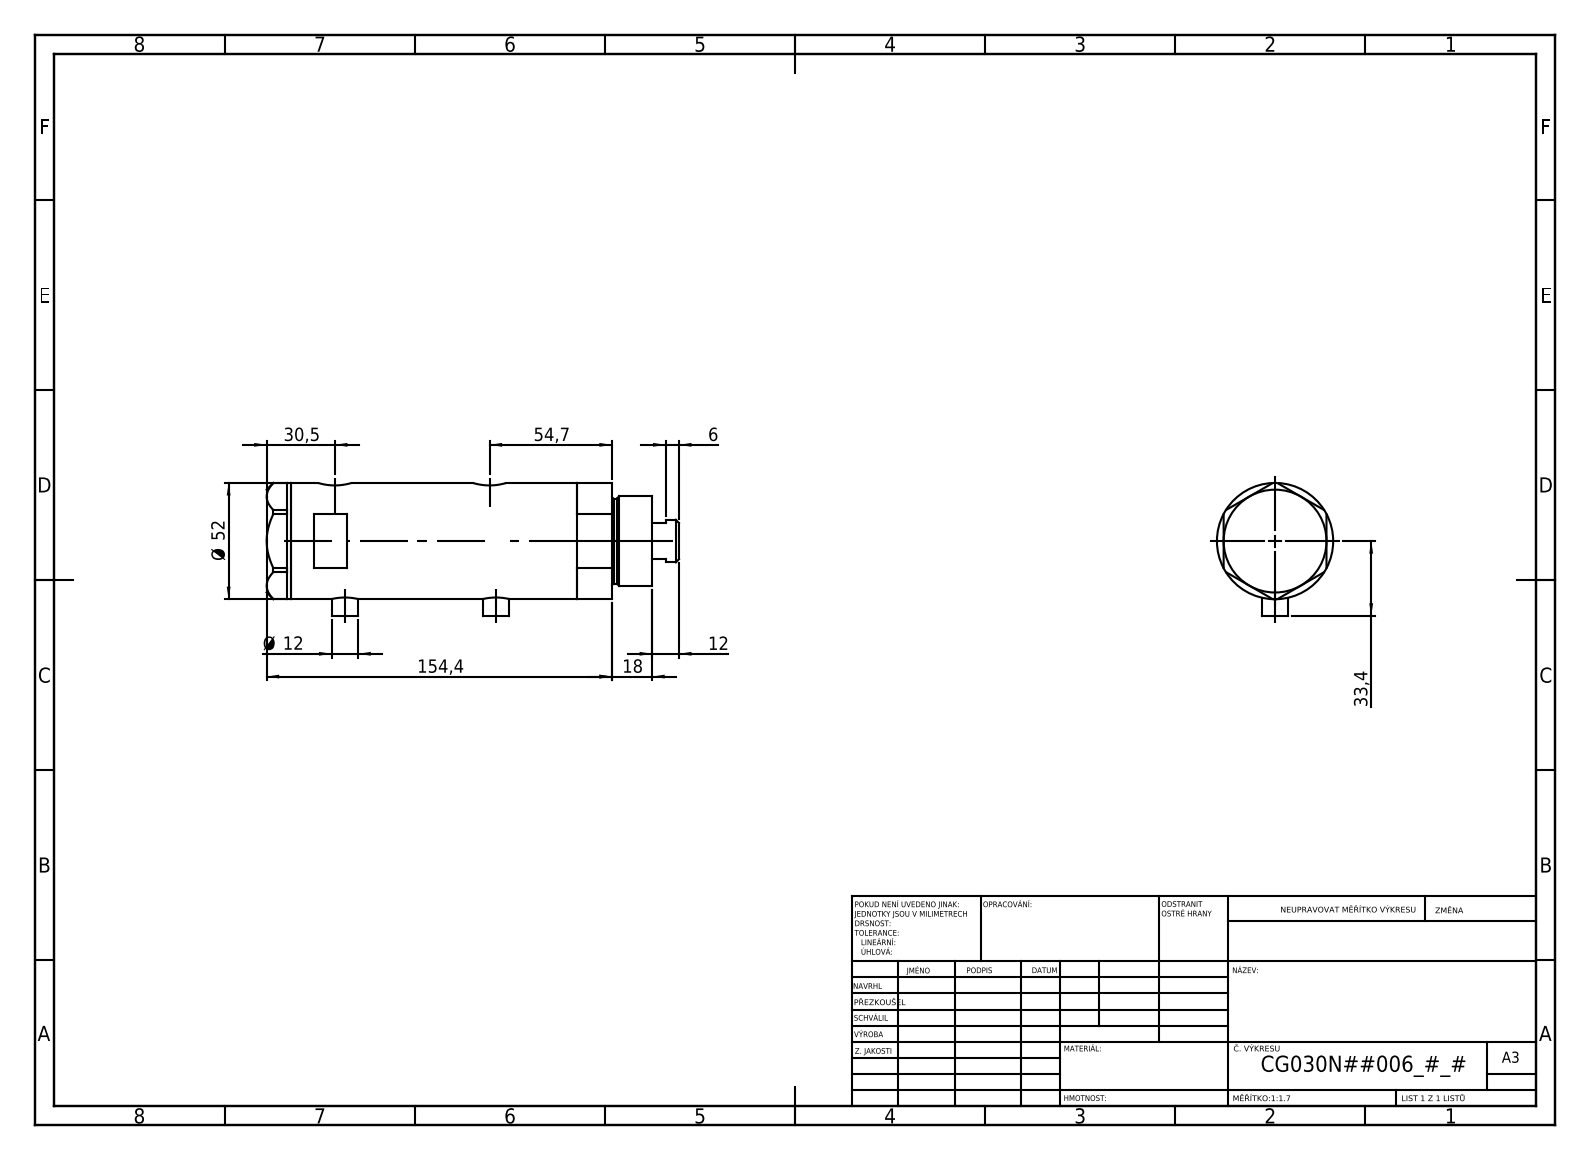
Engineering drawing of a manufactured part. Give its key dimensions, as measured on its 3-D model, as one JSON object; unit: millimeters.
{"part_name": "V270CG_BACK; V270CG_FRONT; V270CG_MIDDLE; V270CG_VC", "step_written_by": "SolidWorks 2019 (CONFIG_CONTROL_DESIGN)", "units": "millimeters", "bodies": {"solids": 4, "faces": 134, "planar": 65, "cylindrical": 49, "other": 20}, "overall_size": [184.4, 59.4, 52], "volume_mm3": 344345, "surface_area_mm2": 77889, "round_holes": [[9.73, 2], [12.5, 2], [15, 2], [6.5, 1], [20, 1], [21.5, 1], [30, 1], [33, 1], [44, 1]], "round_bosses_or_shafts": [[12, 2], [52, 1], [40, 1], [38, 1], [19, 1]], "face_to_face_distances": [91.5, 23.8, 67.7, 11, 34.8, 102.5, 46, 138.9, 127.9, 104.1], "hole_center_spacings": [2.9, 4.5, 64.7, 67.6, 69.2, 72.1]}
